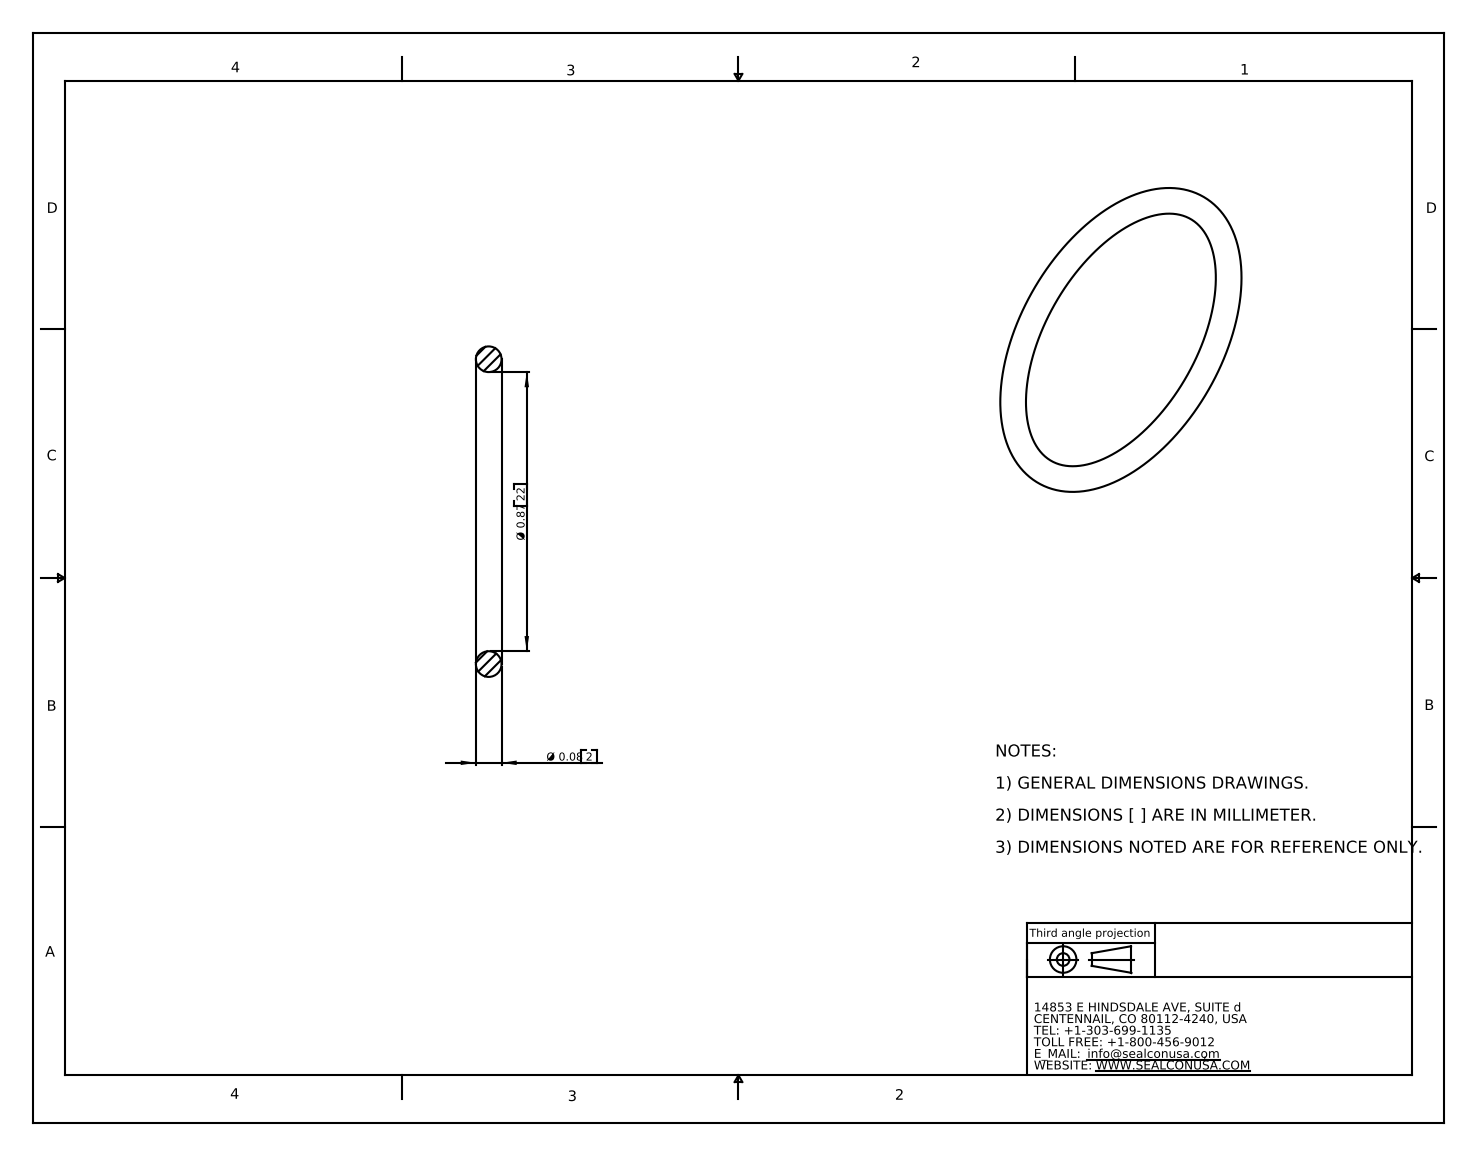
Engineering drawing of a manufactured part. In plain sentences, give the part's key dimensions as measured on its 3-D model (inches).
The part is named "OM-25-BN". Its 3-D file was written by "SolidWorks 2007 (CONFIG_CONTROL_DESIGN)". It is 1 solid with 4 faces: 0 planar, 0 cylindrical and 4 other. Overall it measures 1.03 by 1.03 by 0.08 inches. Its volume is 0.015 cubic inches and its surface area 0.75 square inches.
